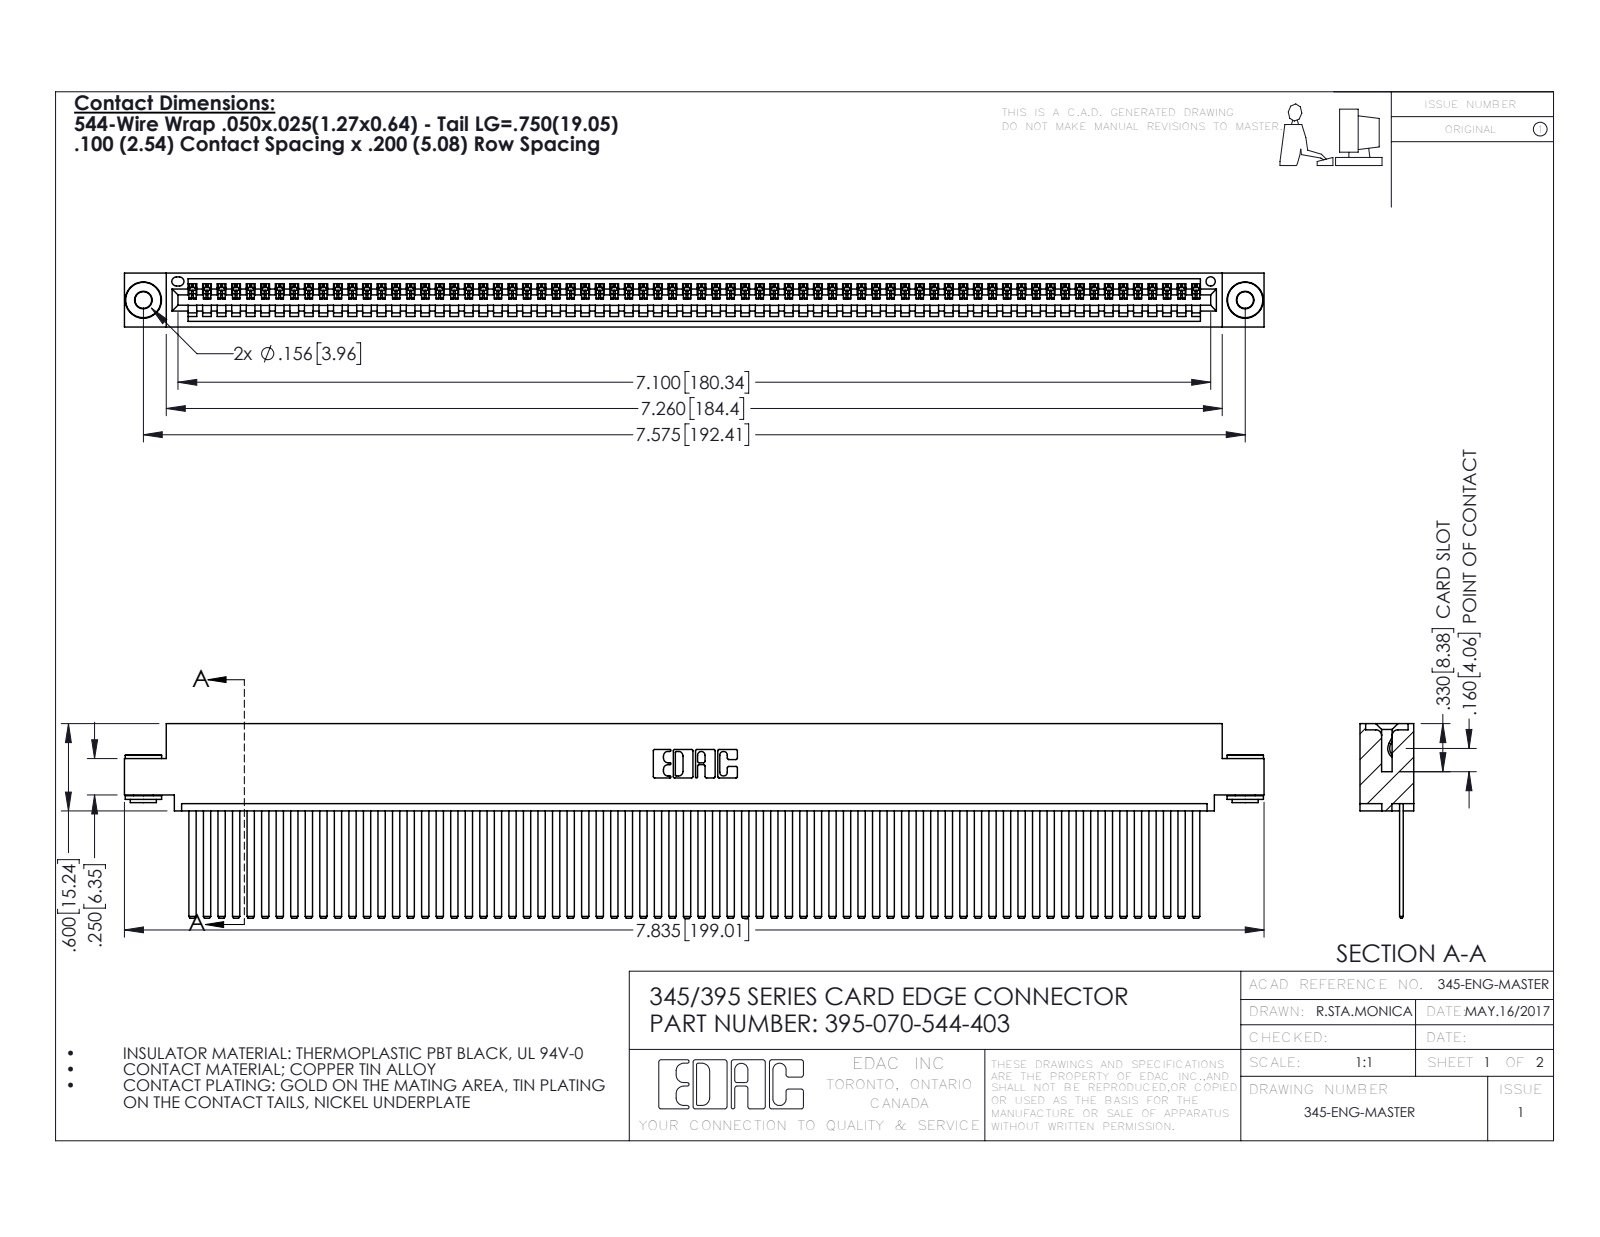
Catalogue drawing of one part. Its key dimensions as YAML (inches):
part_name: "345-292-001_345-293-144; 395-070-544-403; 345 Part_0.110 Offset - 0.156 Dia-TH; 345-250-002_345-250-002-102"
step_written_by: "SolidWorks 2016 (CONFIG_CONTROL_DESIGN)"
units: inches
bodies: {solids: 73, faces: 3808, planar: 2614, cylindrical: 1186, other: 8}
overall_size: [7.835, 1.337, 0.37]
volume: 1.214
surface_area: 45.79
round_holes:
  - {diameter: 0.116, count: 2}
  - {diameter: 0.156, count: 2}
  - {diameter: 0.064, count: 1}
round_bosses_or_shafts:
  - {diameter: 0.25, count: 2}
  - {diameter: 0.18, count: 2}
  - {diameter: 0.136, count: 2}
partial_cylinders:
  - {radius: 0.006, count: 140}
  - {radius: 0.01, count: 22}
  - {radius: 0.007, count: 6}
  - {radius: 0.031, count: 6}
  - {radius: 0.026, count: 3}
  - {radius: 0.031, count: 2}
  - {radius: 0.04, count: 2}
  - {radius: 0.014, count: 1}
face_to_face_distances: [0.072, 0.298, 0.025, 0.098, 0.272, 0.37, 0.2, 0.225, 0.149, 0.072]
hole_center_spacings: [0.27, 7.339, 7.575]
